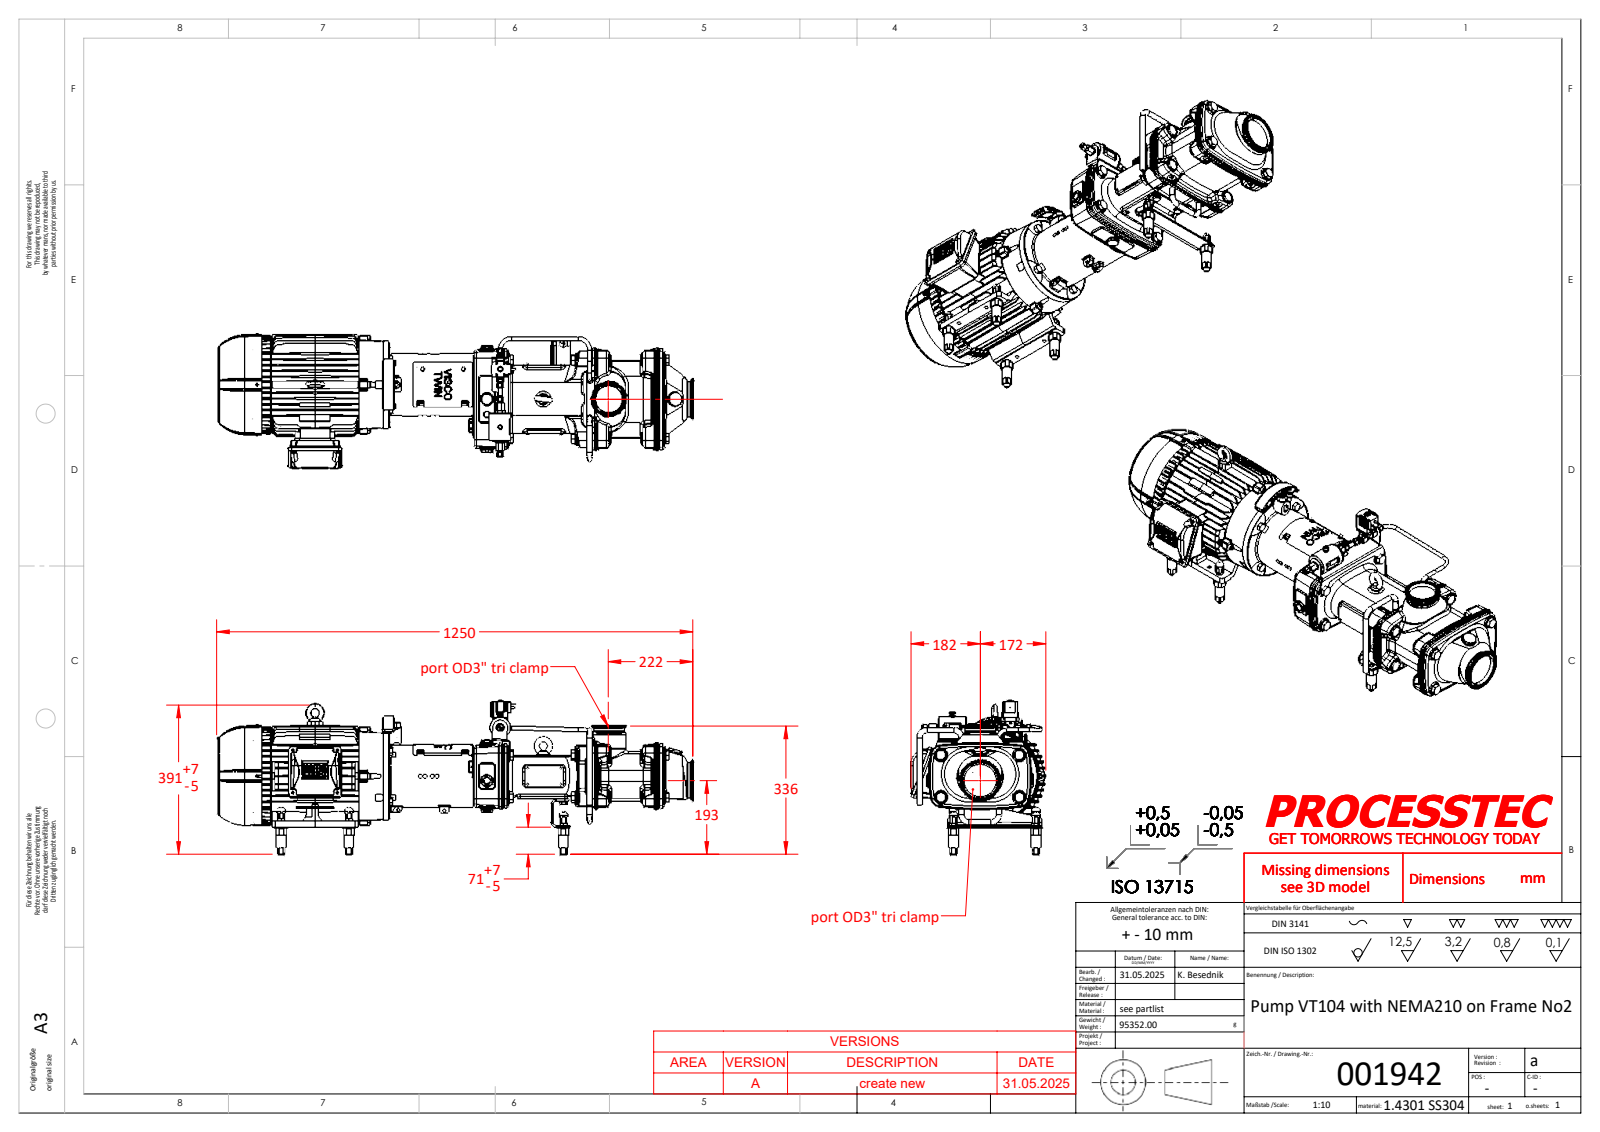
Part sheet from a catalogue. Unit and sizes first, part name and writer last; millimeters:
Units: millimetres
Overall size (bounding box): 1249.74 × 401.96 × 353.85
Round holes (diameter × count): ⌀8 ×13, ⌀5 ×11, ⌀8.5 ×8, ⌀10.41 ×8, ⌀6.2 ×6, ⌀10.2 ×6, ⌀11 ×6, ⌀12 ×6, ⌀22.2 ×6, ⌀4 ×5, ⌀4.35 ×5, ⌀14 ×5
Round bosses / shafts (diameter × count): ⌀10 ×15, ⌀6 ×12, ⌀30 ×10, ⌀24 ×8, ⌀22 ×7, ⌀19 ×6, ⌀5 ×6, ⌀16 ×5
Partial cylindrical surfaces — rounded edges, fillets, slot ends (radius × count): R1 ×1156, R5 ×82, R1.5 ×73, R2 ×60, R3 ×56, R8 ×36, R6 ×26, R10 ×25
Main face-to-face distances: 15, 30, 5.5, 231.3, 605.1, 373.8, 102.4, 20.5, 9.5, 1014.74
Hole centre spacings: 130.23, 38.1, 55, 139.7, 177.8, 28.75, 53.11, 66.62
Volume: 39 960 000 mm³ · Surface area: 2 991 000 mm²
Bodies: 104 solids, 10634 faces (4505 planar, 2805 cylindrical, 3324 other)
Part name (STEP PRODUCT): 001400; 001404; 001403; 001473 (+8 more)
STEP written by: SolidWorks 2023 (AUTOMOTIVE_DESIGN)
